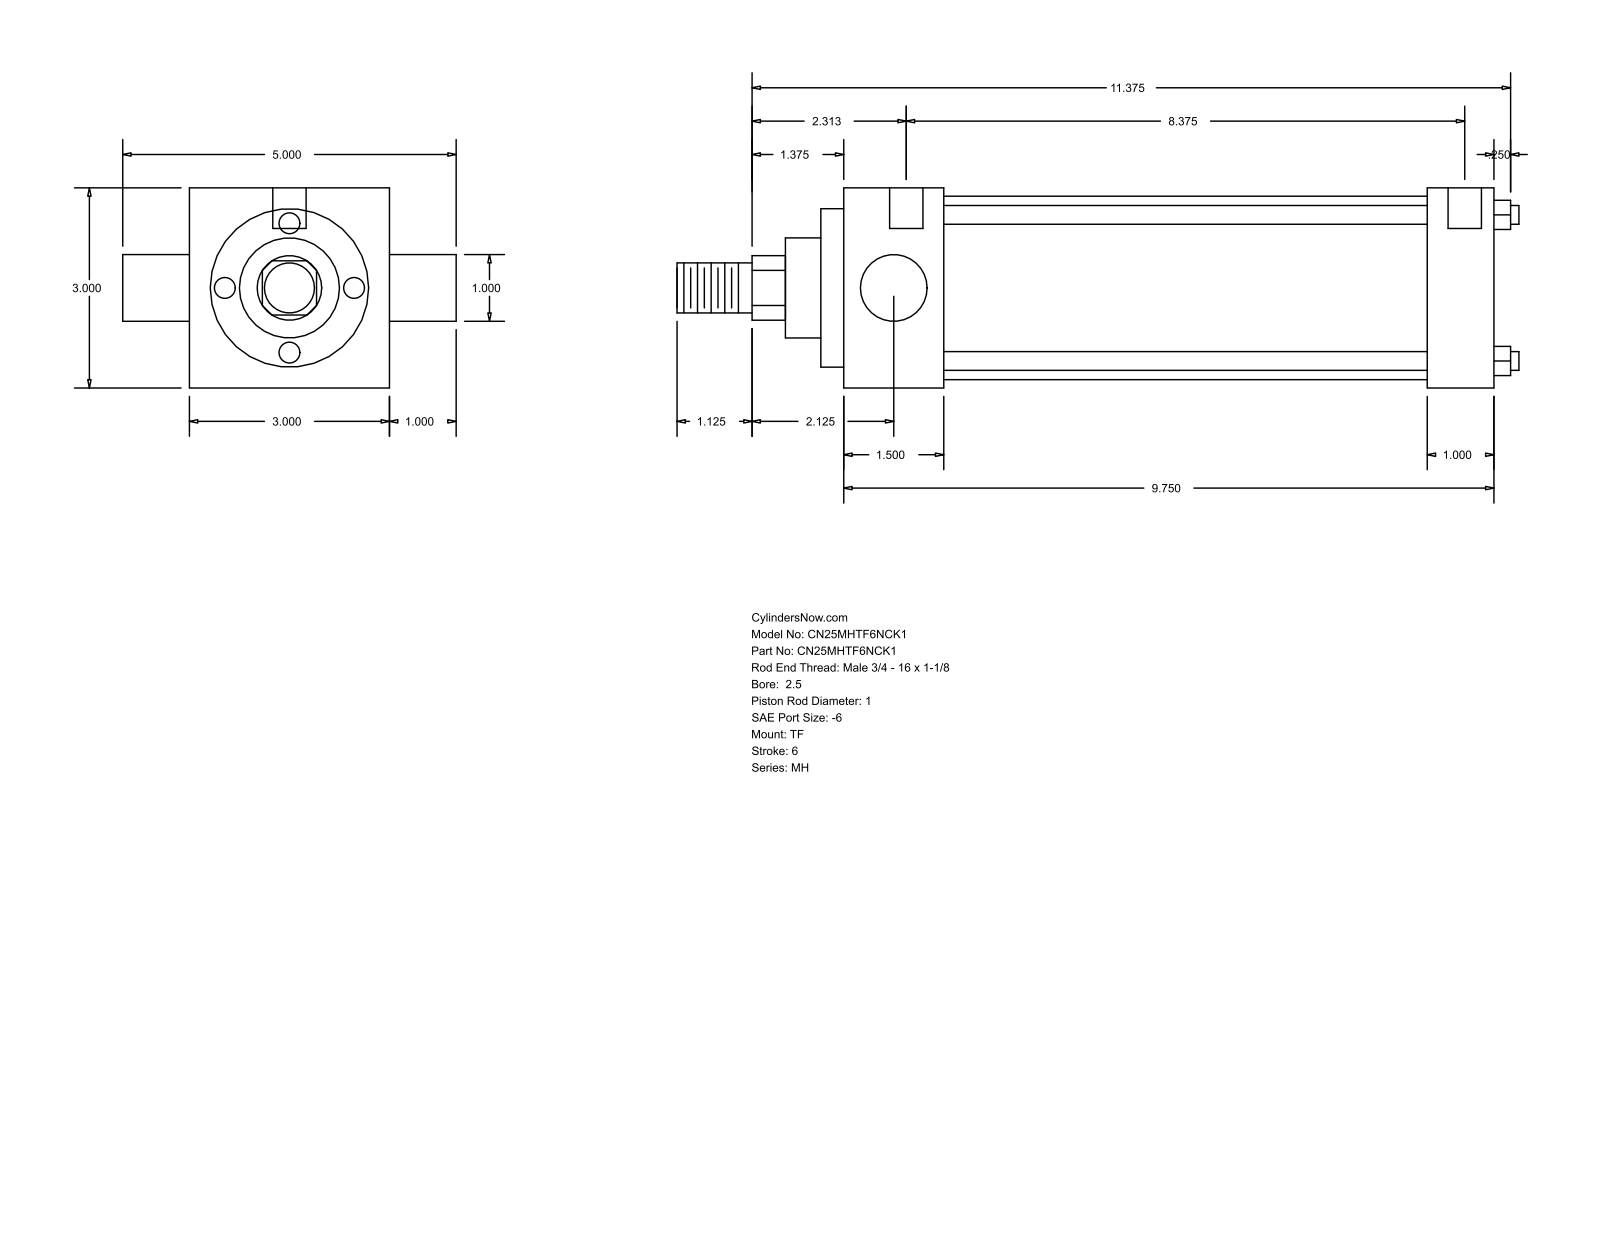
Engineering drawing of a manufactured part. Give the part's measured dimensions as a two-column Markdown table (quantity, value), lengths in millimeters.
| quantity | value |
| --- | --- |
| part name | MH_TF__0250_1 |
| STEP written by | GSSL Pune (CONFIG_CONTROL_DESIGN) |
| units | millimeters |
| bodies | 0 solids, 86 faces (61 planar, 25 cylindrical, 0 other) |
| overall size | 320.68 × 127 × 76.2 |
| round holes (diameter × count) | 5.56 × 3, 12.7 × 2 |
| round bosses / shafts (diameter × count) | 7.14 × 4, 25.4 × 2, 69.85 × 1, 60.33 × 1, 38.1 × 1, 19.05 × 1 |
| partial cylindrical surfaces (radius × count) | 12.29 × 1 |
| main face-to-face distances | 76.2, 247.65, 25.39, 38.11, 209.54, 222.26, 184.15, 8.73, 46.84, 230.99 |
| hole center spacings | 3.18, 4.76, 212.72, 215.9, 217.48, 220.66 |
